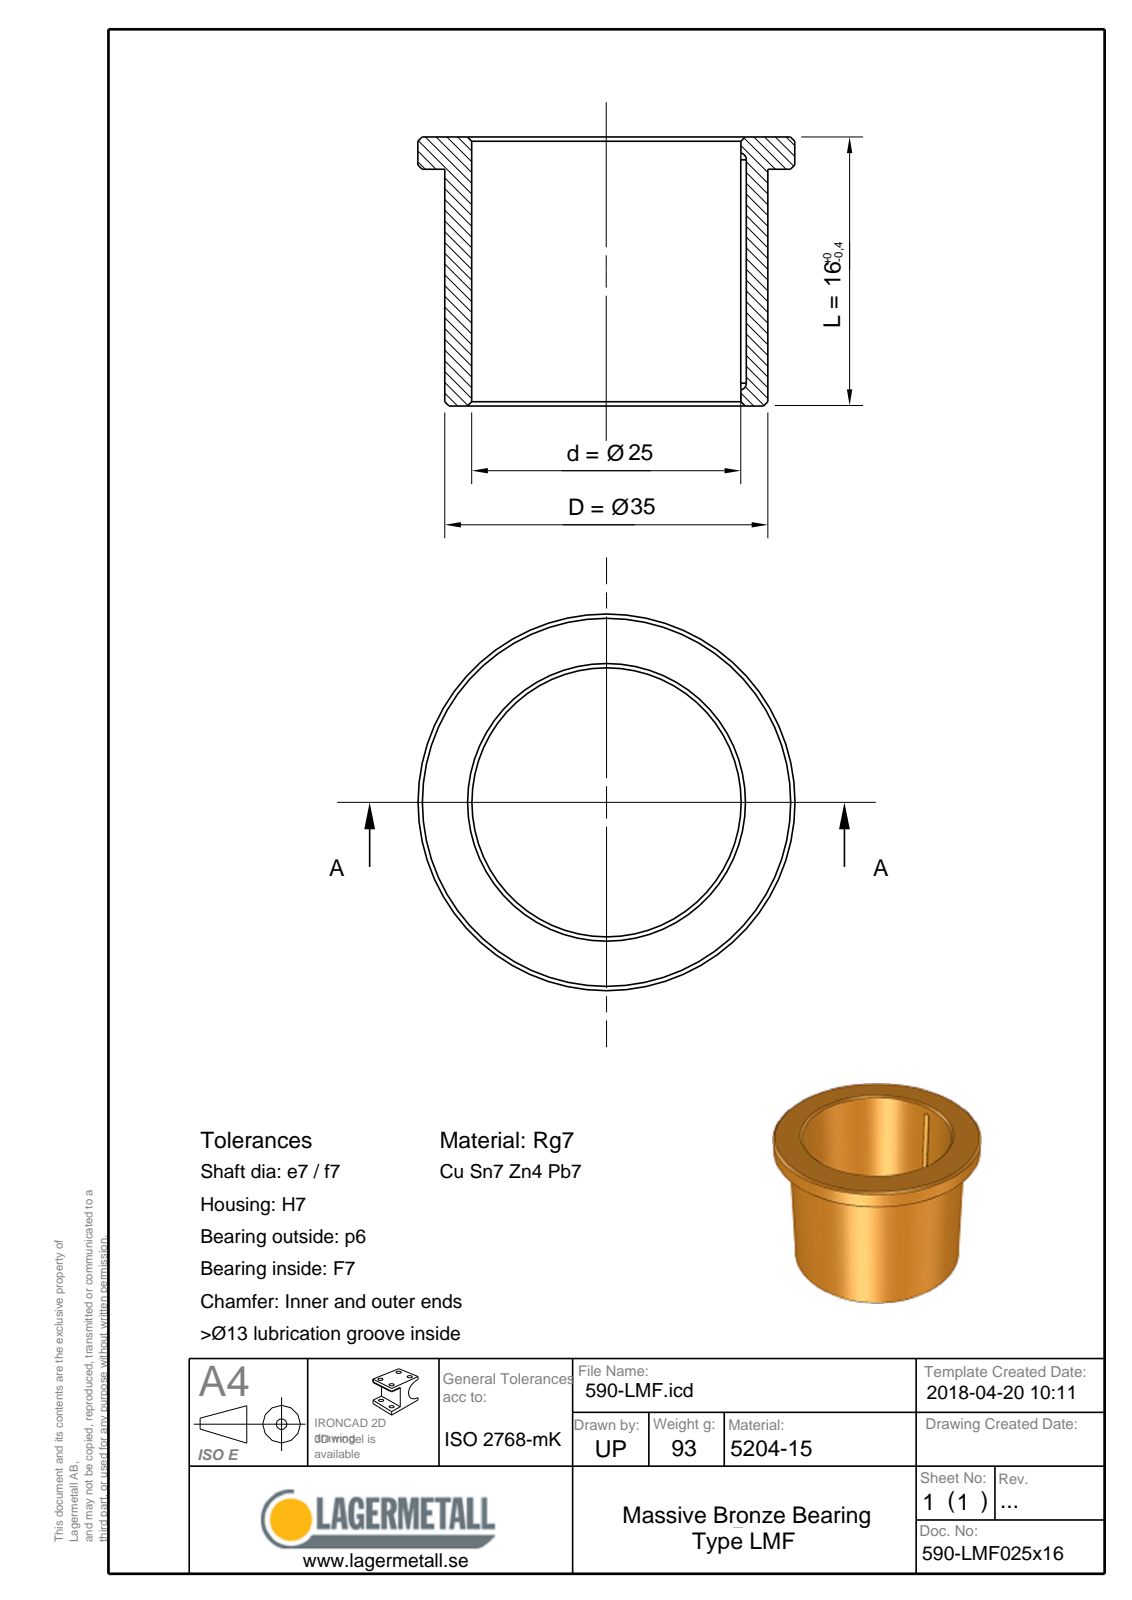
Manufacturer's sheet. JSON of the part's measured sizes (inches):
{"part_name": "590-LMF025x16", "step_written_by": "Spatial InterOp 3D (CONFIG_CONTROL_DESIGN)", "units": "inches", "bodies": {"solids": 1, "faces": 16, "planar": 4, "cylindrical": 5, "other": 7}, "overall_size": [1.772, 1.772, 0.63], "volume_in3": 0.647, "surface_area_in2": 8.094, "round_holes": [[0.984, 1]], "round_bosses_or_shafts": [[1.772, 1], [1.378, 1]], "partial_cylinders_radius": [[0.049, 2]], "face_to_face_distances": [0.197, 0.433, 0.63]}
